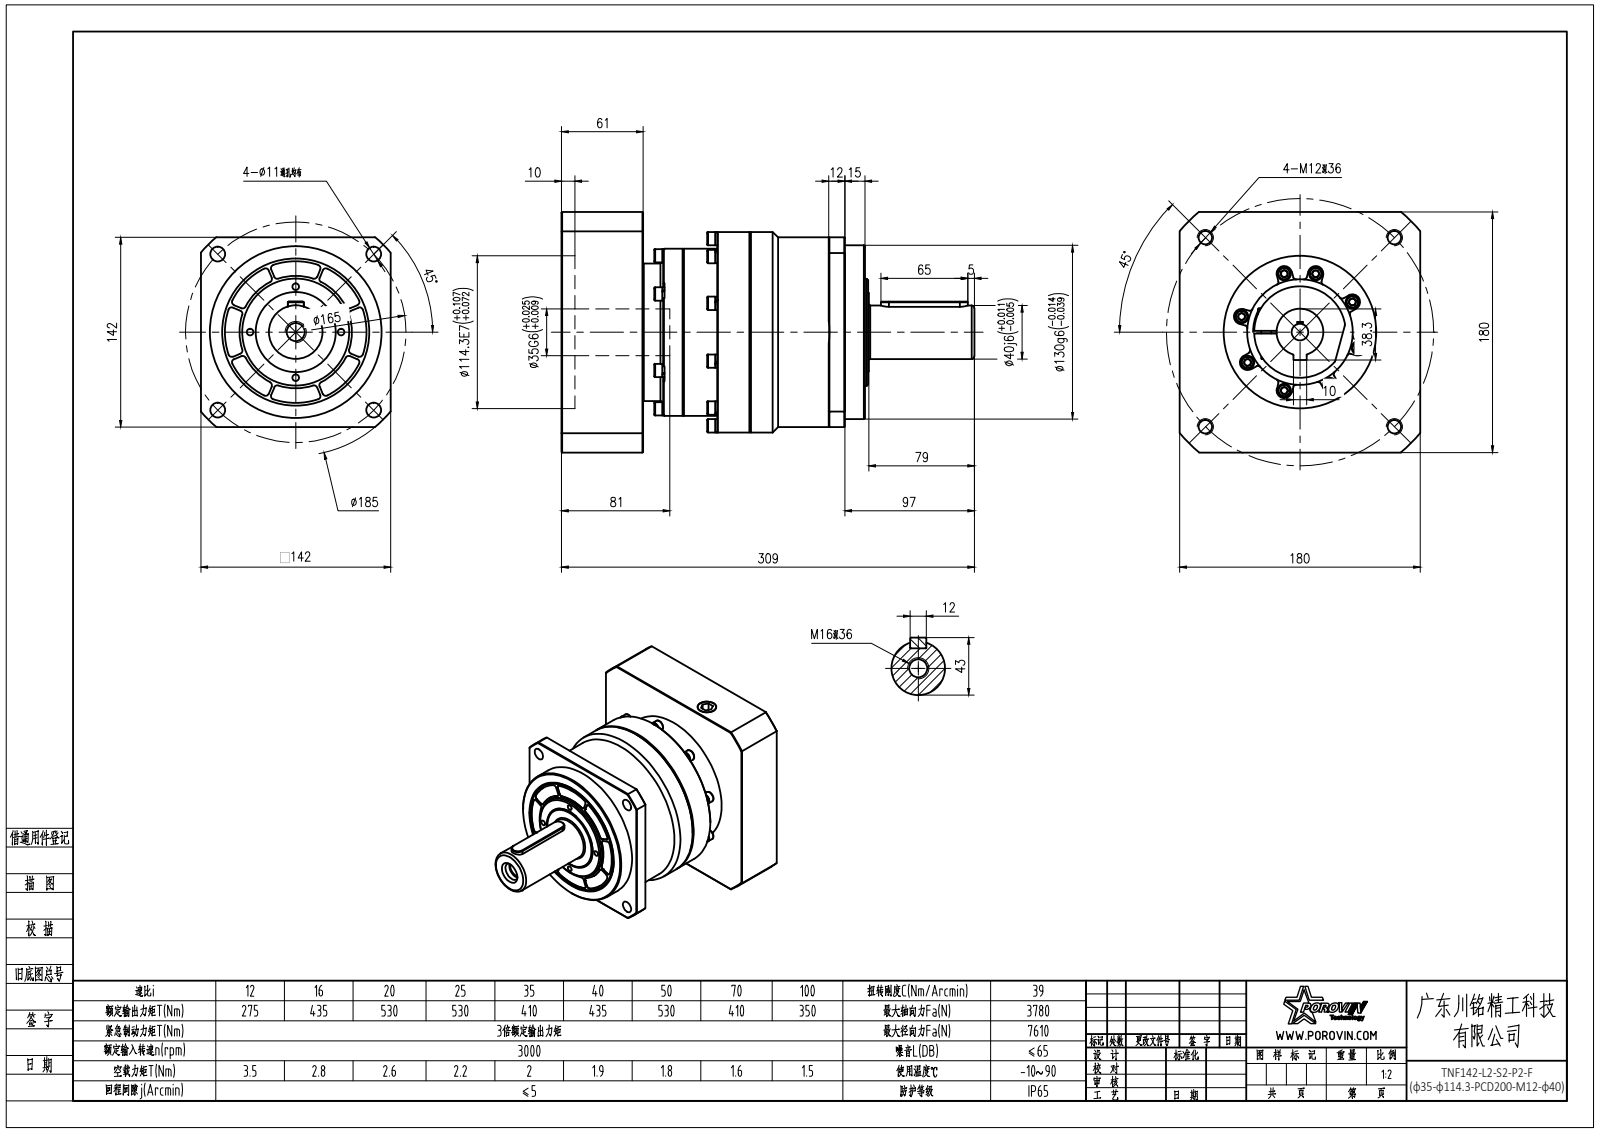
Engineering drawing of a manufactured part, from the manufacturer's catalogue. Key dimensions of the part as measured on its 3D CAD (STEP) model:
Part name (STEP PRODUCT): 二级齿圈KD140外形图; 一级齿圈加出轴KS142外形图; hex socket set screws with flat point gb_GB_FASTENER_SCREWS_HSFP M16X16-N; hexagon socket head cap screws gb_GB_FASTENER_SCREWS_HSHCS M6X20-N (+3 more)
STEP written by: SolidWorks 2016 (CONFIG_CONTROL_DESIGN)
Units: millimetres
Bodies: 51 solids, 1355 faces (594 planar, 483 cylindrical, 278 other)
Overall size (bounding box): 309 × 180 × 180
Volume: 4 003 000 mm³ · Surface area: 378 428 mm²
Round holes (diameter × count): ⌀6.68 ×22, ⌀5 ×16, ⌀6.6 ×16, ⌀6.5 ×6, ⌀10.2 ×4, ⌀11 ×4, ⌀14 ×2, ⌀6.8 ×1, ⌀9 ×1, ⌀13.6 ×1, ⌀17 ×1, ⌀35 ×1
Round bosses / shafts (diameter × count): ⌀10 ×22, ⌀9.88 ×22, ⌀6 ×22, ⌀150 ×1, ⌀142 ×1, ⌀130 ×1, ⌀125 ×1, ⌀103 ×1
Partial cylindrical surfaces — rounded edges, fillets, slot ends (radius × count): R2 ×44, R5.5 ×6, R5.75 ×6, R6 ×2, R42.5 ×1, R51 ×1, R92.5 ×1, R117.5 ×1
Main face-to-face distances: 80, 30, 61, 141, 50, 91, 180, 15, 32.5, 151
Hole centre spacings: 57.25, 70, 43.26, 62.84, 82.29, 110.07, 35, 87.4
